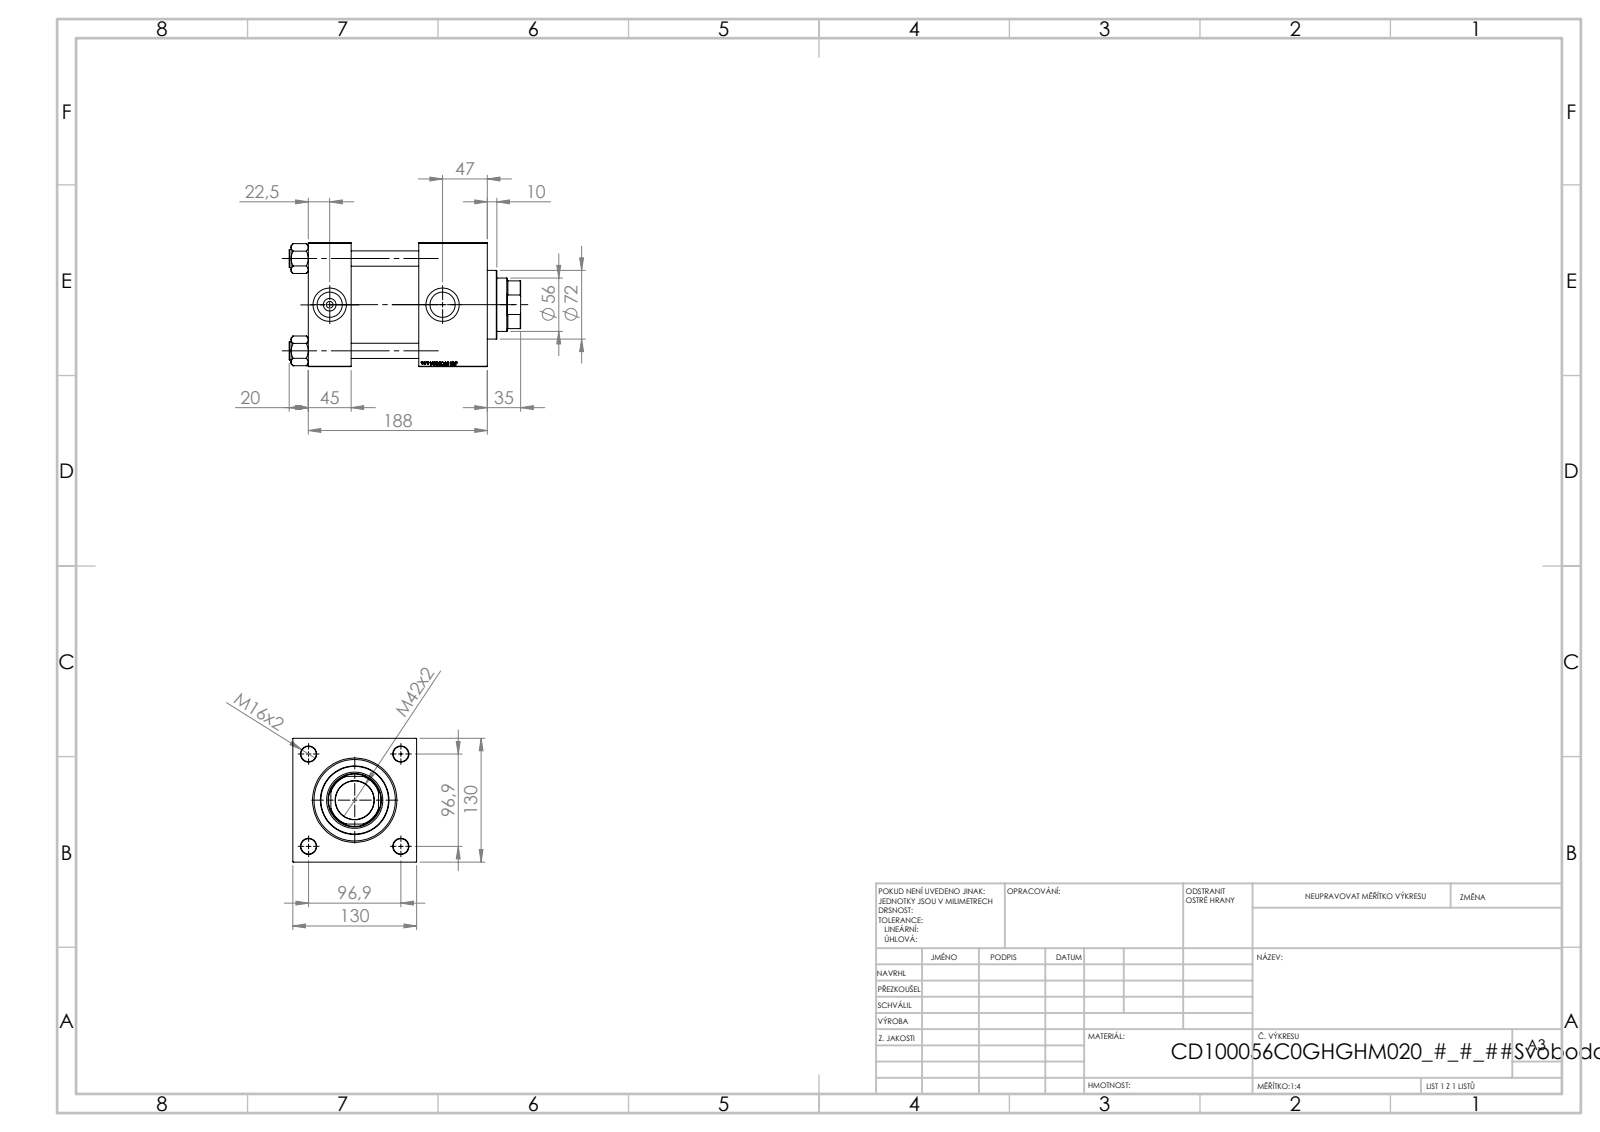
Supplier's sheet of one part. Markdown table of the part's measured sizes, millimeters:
| quantity | value |
| --- | --- |
| part name | NUT_M5_V215CD_C; V215CD_VC_C; V215CD_C_TYCINKA; V215CD_VCP_C (+1 more) |
| STEP written by | SolidWorks 2019 (CONFIG_CONTROL_DESIGN) |
| units | millimeters |
| bodies | 11 solids, 1196 faces (574 planar, 86 cylindrical, 536 other) |
| overall size | 243 × 130 × 130 |
| volume | 2 475 000 mm³ |
| surface area | 333 370 mm² |
| round holes (diameter × count) | 16 × 4, 7 × 2, 26.44 × 2, 35 × 2, 40.5 × 1, 56 × 1, 59 × 1, 76 × 1, 85.5 × 1, 100 × 1 |
| round bosses / shafts (diameter × count) | 19 × 4, 106 × 1, 72 × 1 |
| partial cylindrical surfaces (radius × count) | 27 × 1 |
| main face-to-face distances | 130, 45, 188, 143, 116, 71, 72, 20, 51, 96 |
| hole center spacings | 68.52, 96.9, 137.04, 118.5 |
